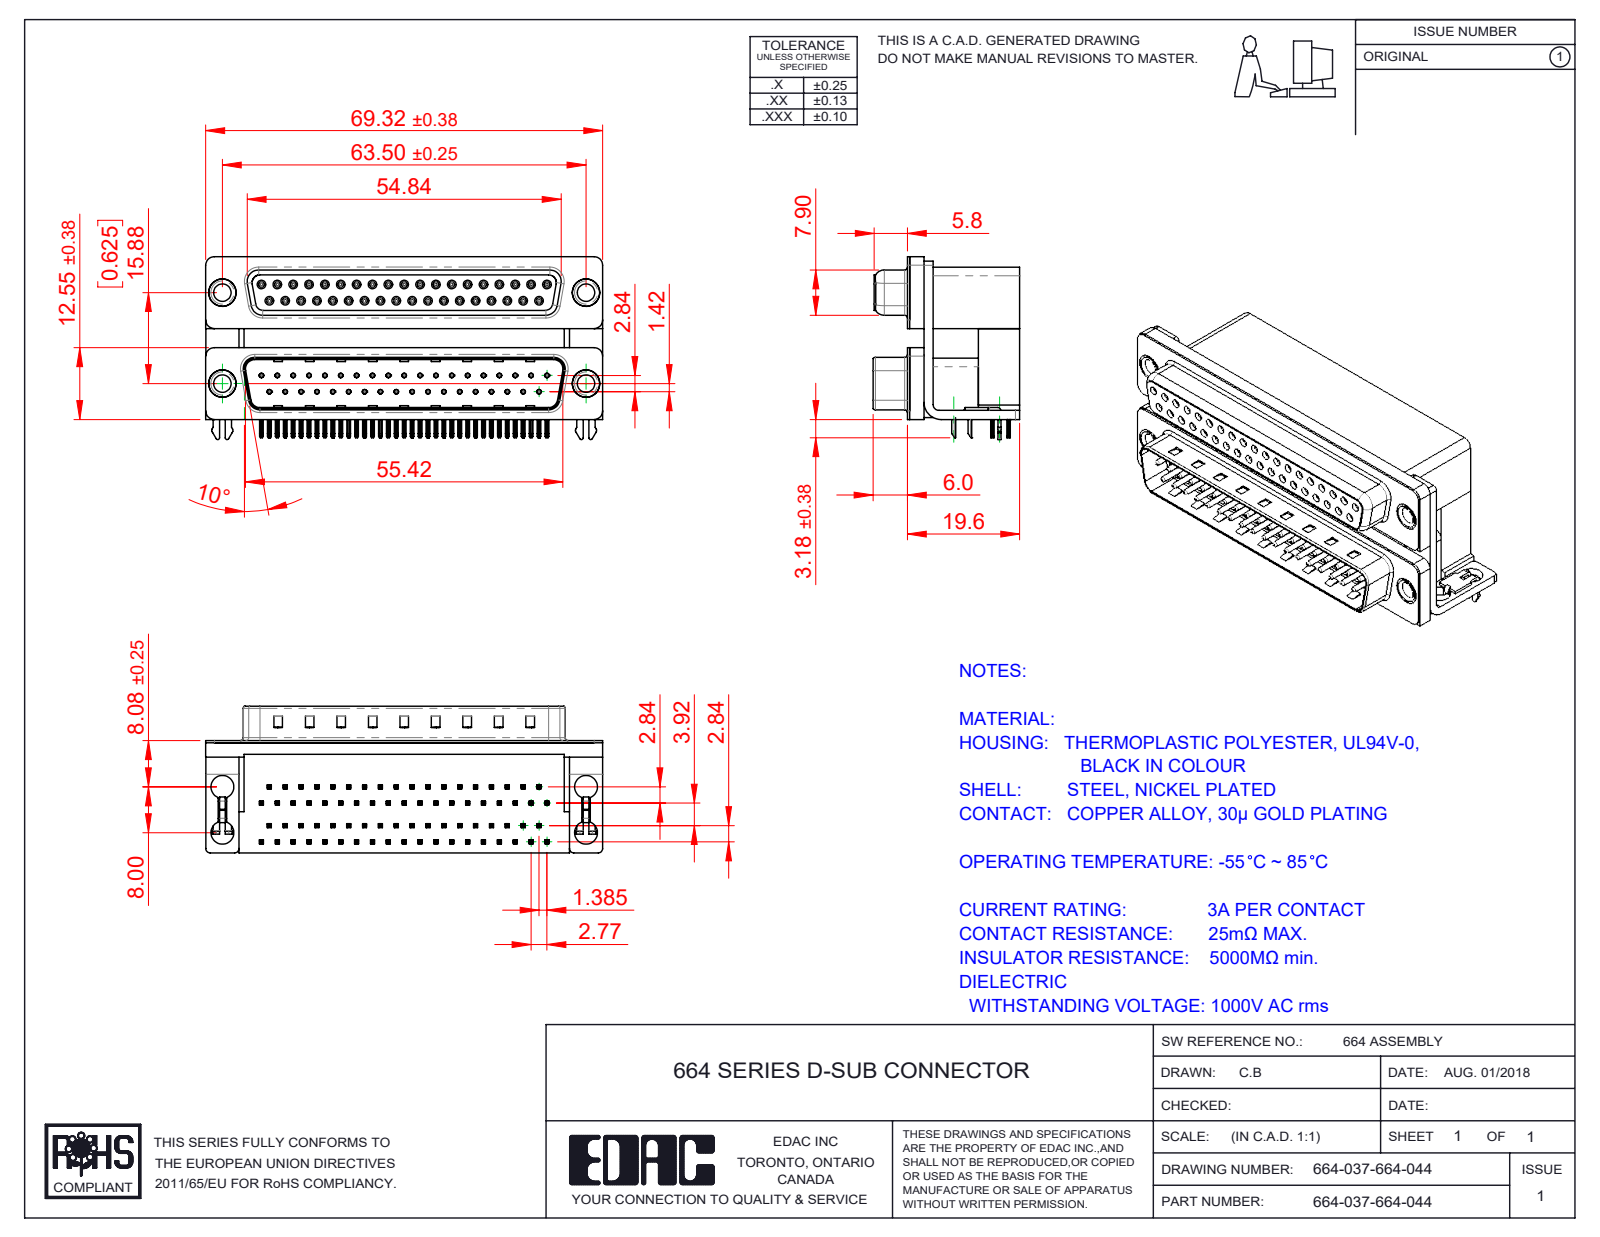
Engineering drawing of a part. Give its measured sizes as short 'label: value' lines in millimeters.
name: 664 Mounting Bracket_2ProngL; 664-037-664-044; 664 Housing Spacer_37 Contacts L; 664 Contact Top Lower (+8 more)
written by: SolidWorks 2020 (CONFIG_CONTROL_DESIGN)
unit: mm
bodies: 87 solids, 8969 faces (4819 planar, 2171 cylindrical, 1979 other)
size: 69.32 × 31.93 × 25.6
volume: 29 759 mm³; area: 31 558 mm²
holes: 74× ⌀0.8, 37× ⌀0.35, 37× ⌀0.9, 8× ⌀4, 4× ⌀3.05, 4× ⌀3.5, 4× ⌀4.8, 4× ⌀5
bosses: 37× ⌀1.2, 37× ⌀0.75, 4× ⌀4.9, 4× ⌀4.75, 4× ⌀3.85
rounds: 297× R0.1, 154× R0.25, 148× R0.15, 74× R0.12, 74× R0.35, 37× R0.34, 18× R0.28, 16× R0.5
face distances: 0.4, 19.2, 7.2, 12, 2.19, 15.52, 2.84, 26.22, 10.7, 13.33
hole spacings: 2.77, 5.54, 3.16, 8.31, 11.08, 13.85, 16.62, 19.39
